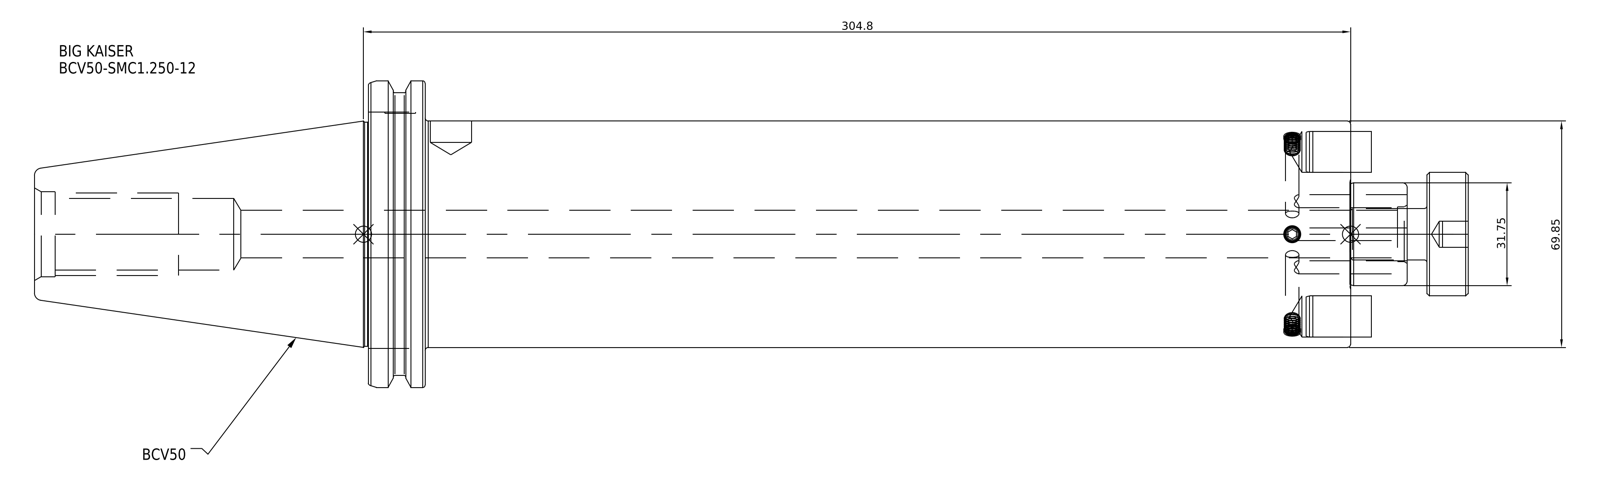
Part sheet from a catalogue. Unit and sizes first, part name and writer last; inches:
Units: inches
Overall size (bounding box): 16.252 × 3.875 × 3.875
Round holes (diameter × count): ⌀0.578 ×1
Round bosses / shafts (diameter × count): ⌀3.875 ×1, ⌀3.594 ×1, ⌀2.75 ×1
Main face-to-face distances: 0.691, 11.25, 11.941, 16, 4.75, 4.059, 0.5, 0.252, 11.502, 12.193
Volume: 87.45 in³ · Surface area: 175.6 in²
Bodies: 1 solid, 35 faces (17 planar, 12 cylindrical, 6 other)
Part name (STEP PRODUCT): BCV50-SMC1_250-12
STEP written by: SolidWorks 2021 (CONFIG_CONTROL_DESIGN)
